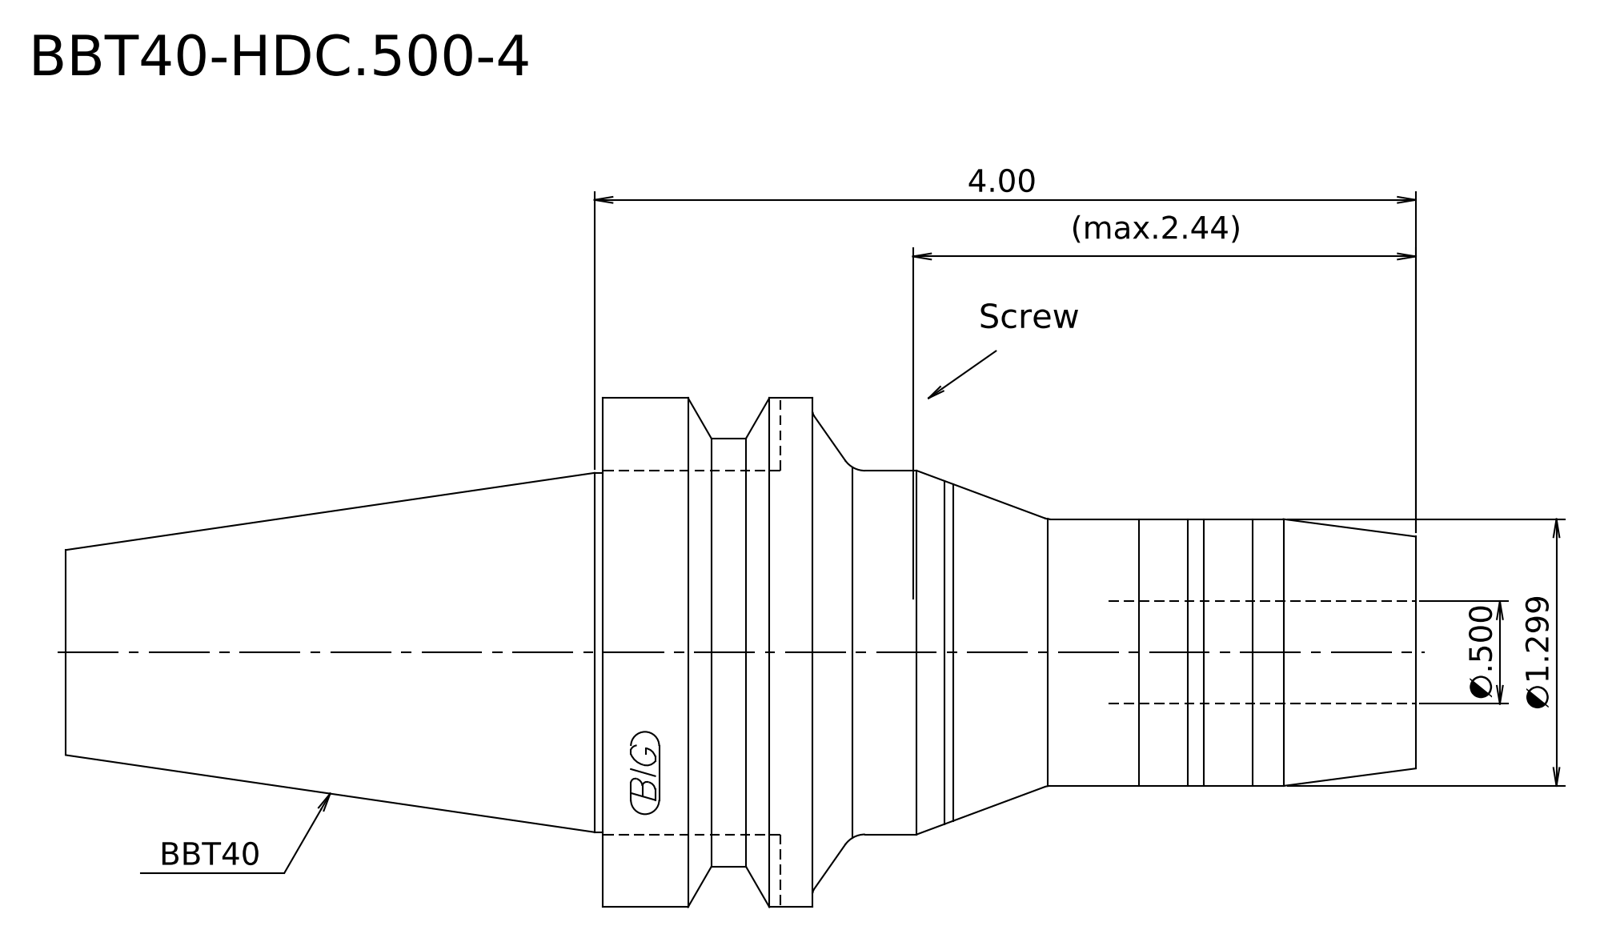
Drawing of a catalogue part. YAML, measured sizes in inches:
step_written_by: "Kubotek KeyCreator 2011 V10.0.2 (22737) (automotive_design)"
units: inches
bodies: {solids: 1, faces: 16, planar: 4, cylindrical: 6, other: 6}
overall_size: [6.575, 2.48, 2.48]
volume: 13.48
surface_area: 39.77
round_bosses_or_shafts:
  - {diameter: 2.48, count: 1}
  - {diameter: 2.087, count: 1}
  - {diameter: 1.772, count: 1}
  - {diameter: 1.75, count: 1}
  - {diameter: 1.299, count: 1}
face_to_face_distances: [3.961, 6.575, 2.614, 2.937, 1.024, 3.638]
